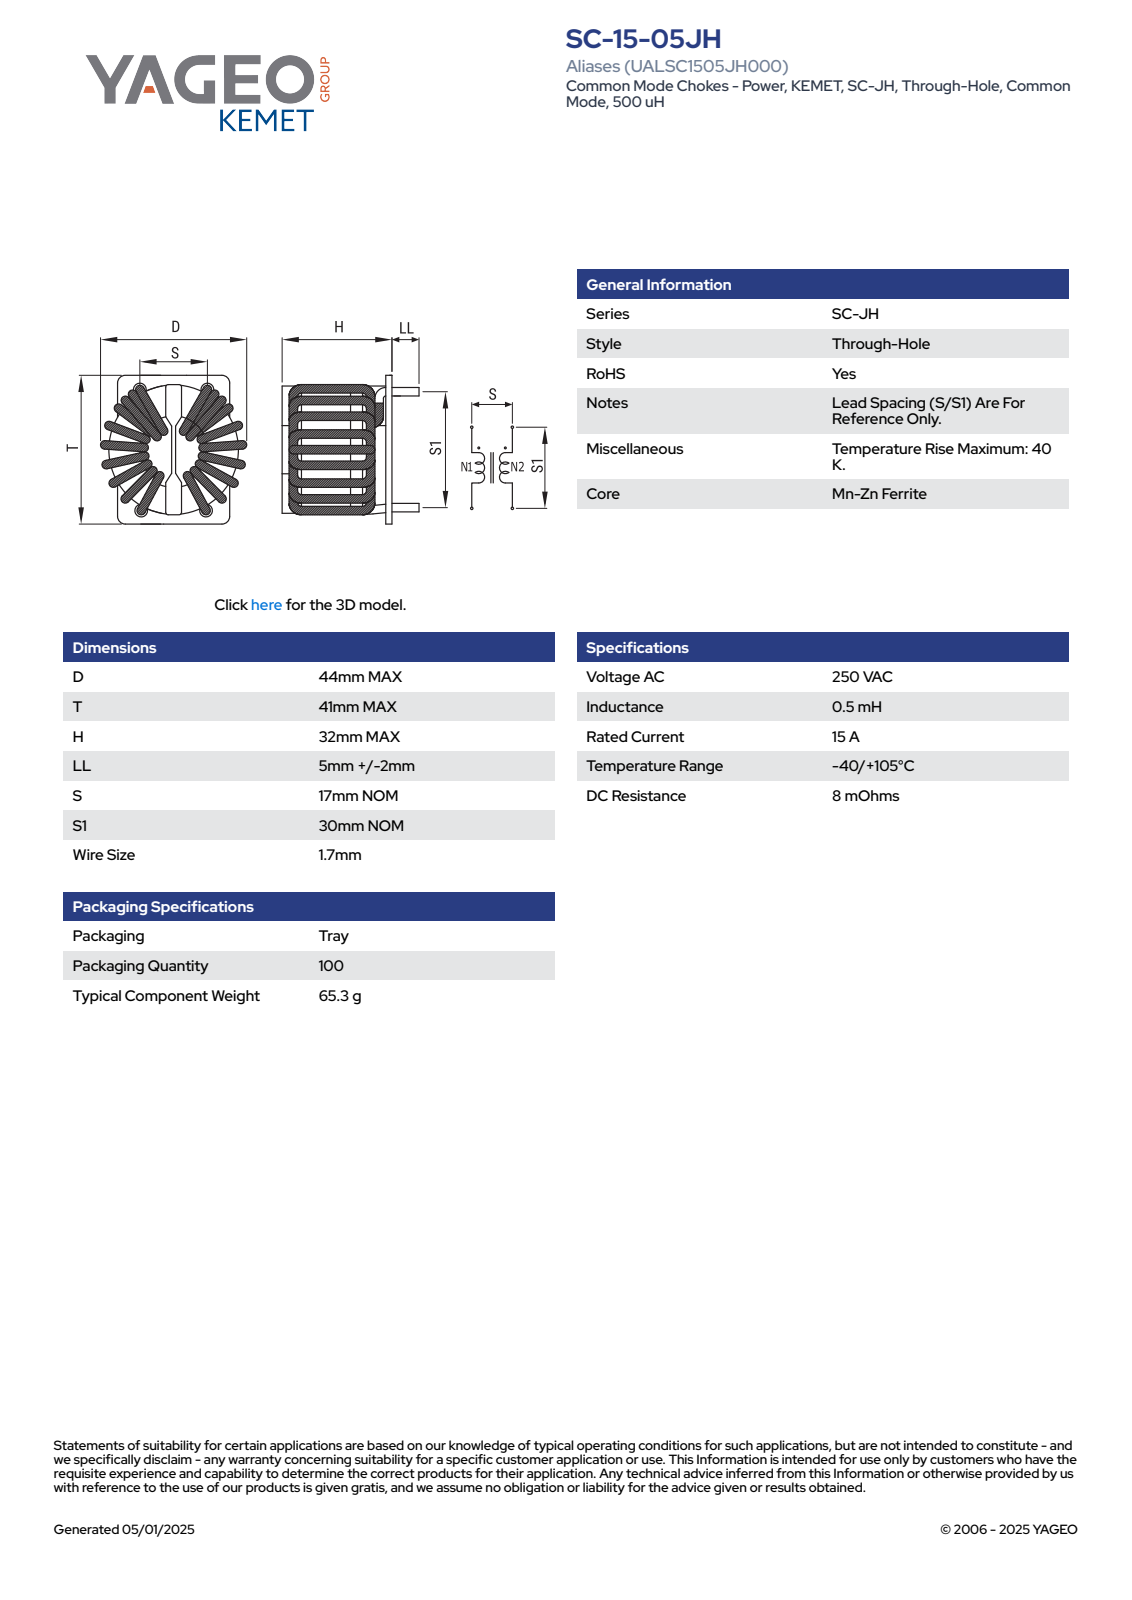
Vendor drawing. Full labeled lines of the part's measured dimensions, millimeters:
Part name (STEP PRODUCT): SC-15-05JH
STEP written by: SolidWorks 2018 (AUTOMOTIVE_DESIGN)
Units: millimetres
Bodies: 1 solid, 510 faces (240 planar, 158 cylindrical, 112 other)
Overall size (bounding box): 44 × 41 × 37
Volume: 30 551 mm³ · Surface area: 14 338 mm²
Round holes (diameter × count): ⌀2.2 ×4
Round bosses / shafts (diameter × count): ⌀1.7 ×10
Partial cylindrical surfaces — rounded edges, fillets, slot ends (radius × count): R0.5 ×30, R0.85 ×28, R0.8 ×8, R6 ×4, R0.4 ×2, R1 ×2, R6.6 ×1, R8.8 ×1
Main face-to-face distances: 3.2, 27.2, 7.6, 4.4, 30.4, 22.8, 1.3, 1, 2.4, 1.1
Hole centre spacings: 17, 30, 34.48
